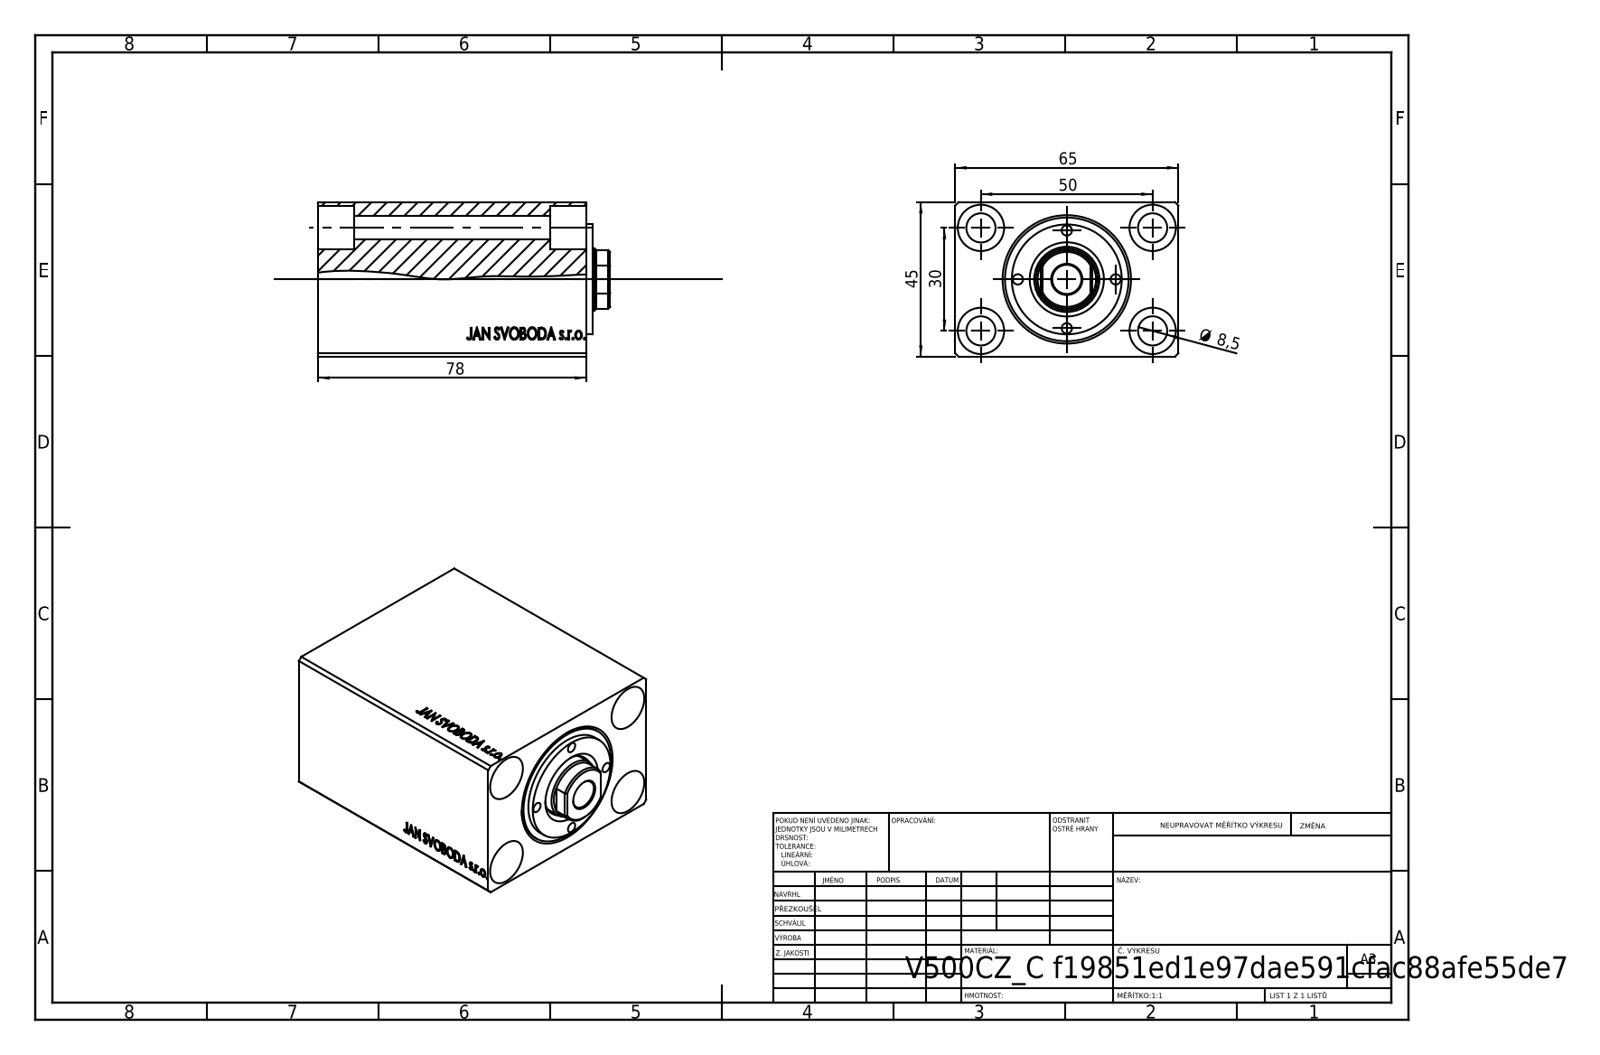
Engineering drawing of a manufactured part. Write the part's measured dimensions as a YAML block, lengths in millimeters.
step_written_by: "SolidWorks 2019 (CONFIG_CONTROL_DESIGN)"
units: millimeters
bodies: {solids: 1, faces: 818, planar: 394, cylindrical: 42, other: 382}
overall_size: [78, 65, 45]
volume: 135599
surface_area: 40548
round_holes:
  - {diameter: 8.5, count: 4}
  - {diameter: 13.5, count: 4}
  - {diameter: 5.5, count: 2}
  - {diameter: 13.6, count: 2}
  - {diameter: 20, count: 2}
  - {diameter: 25, count: 1}
  - {diameter: 36, count: 1}
face_to_face_distances: [45, 65, 78, 77.8, 10.33, 67.67, 58, 19.8, 20, 8.5]
hole_center_spacings: [29.15, 30, 50, 58.31, 45]
